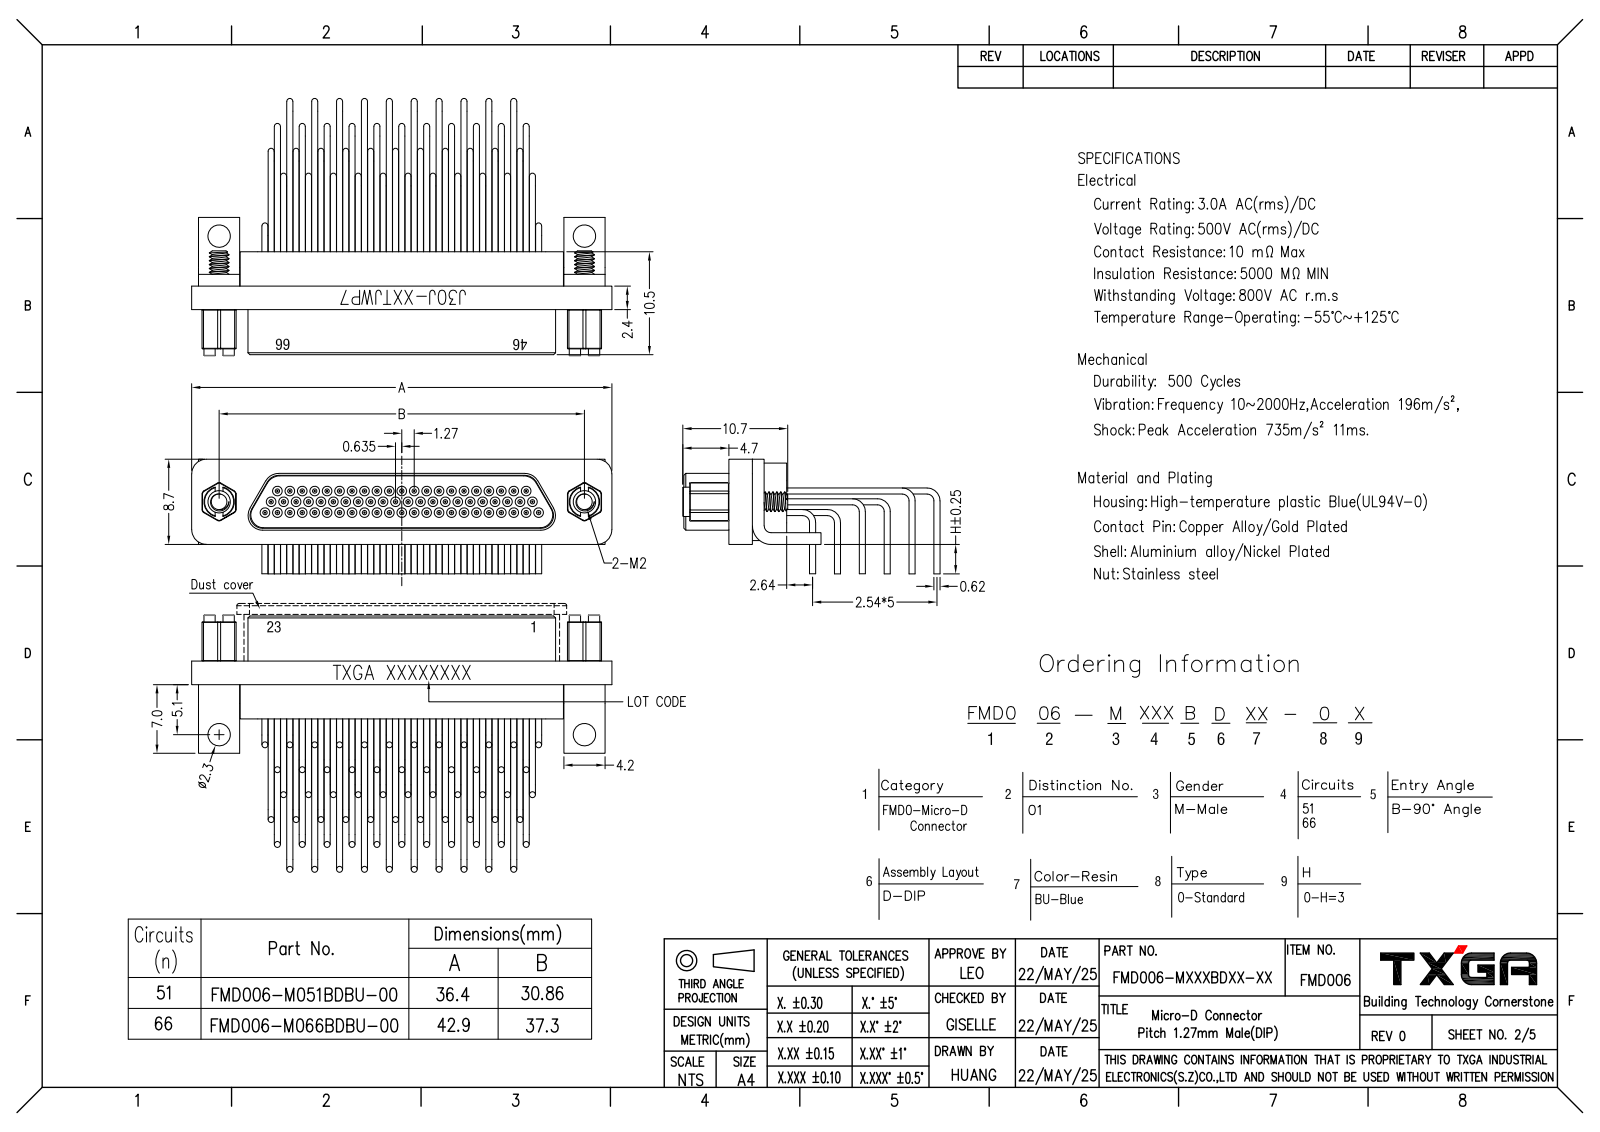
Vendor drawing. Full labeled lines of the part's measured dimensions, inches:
Part name (STEP PRODUCT): FMD006-M009BDBU-00
STEP written by: SolidWorks 2021 (CONFIG_CONTROL_DESIGN)
Units: inches
Bodies: 1 solid, 1079 faces (521 planar, 222 cylindrical, 336 other)
Overall size (bounding box): 0.83 × 0.772 × 0.417
Volume: 0.057 in³ · Surface area: 2.248 in²
Round holes (diameter × count): ⌀0.039 ×9, ⌀0.063 ×2, ⌀0.071 ×2, ⌀0.091 ×2
Round bosses / shafts (diameter × count): ⌀0.024 ×18, ⌀0.018 ×9, ⌀0.122 ×2, ⌀0.079 ×2
Partial cylindrical surfaces — rounded edges, fillets, slot ends (radius × count): R0.012 ×12, R0.059 ×10, R0.071 ×4, R0.045 ×2, R0.051 ×2, R0.028 ×1, R0.075 ×1
Main face-to-face distances: 0.047, 0.232, 0.138, 0.142, 0.283, 0.563, 0.016, 0.299, 0.091, 0.252
Hole centre spacings: 0.05, 0.087, 0.132, 0.1, 0.1, 0.15, 0.18, 0.183
